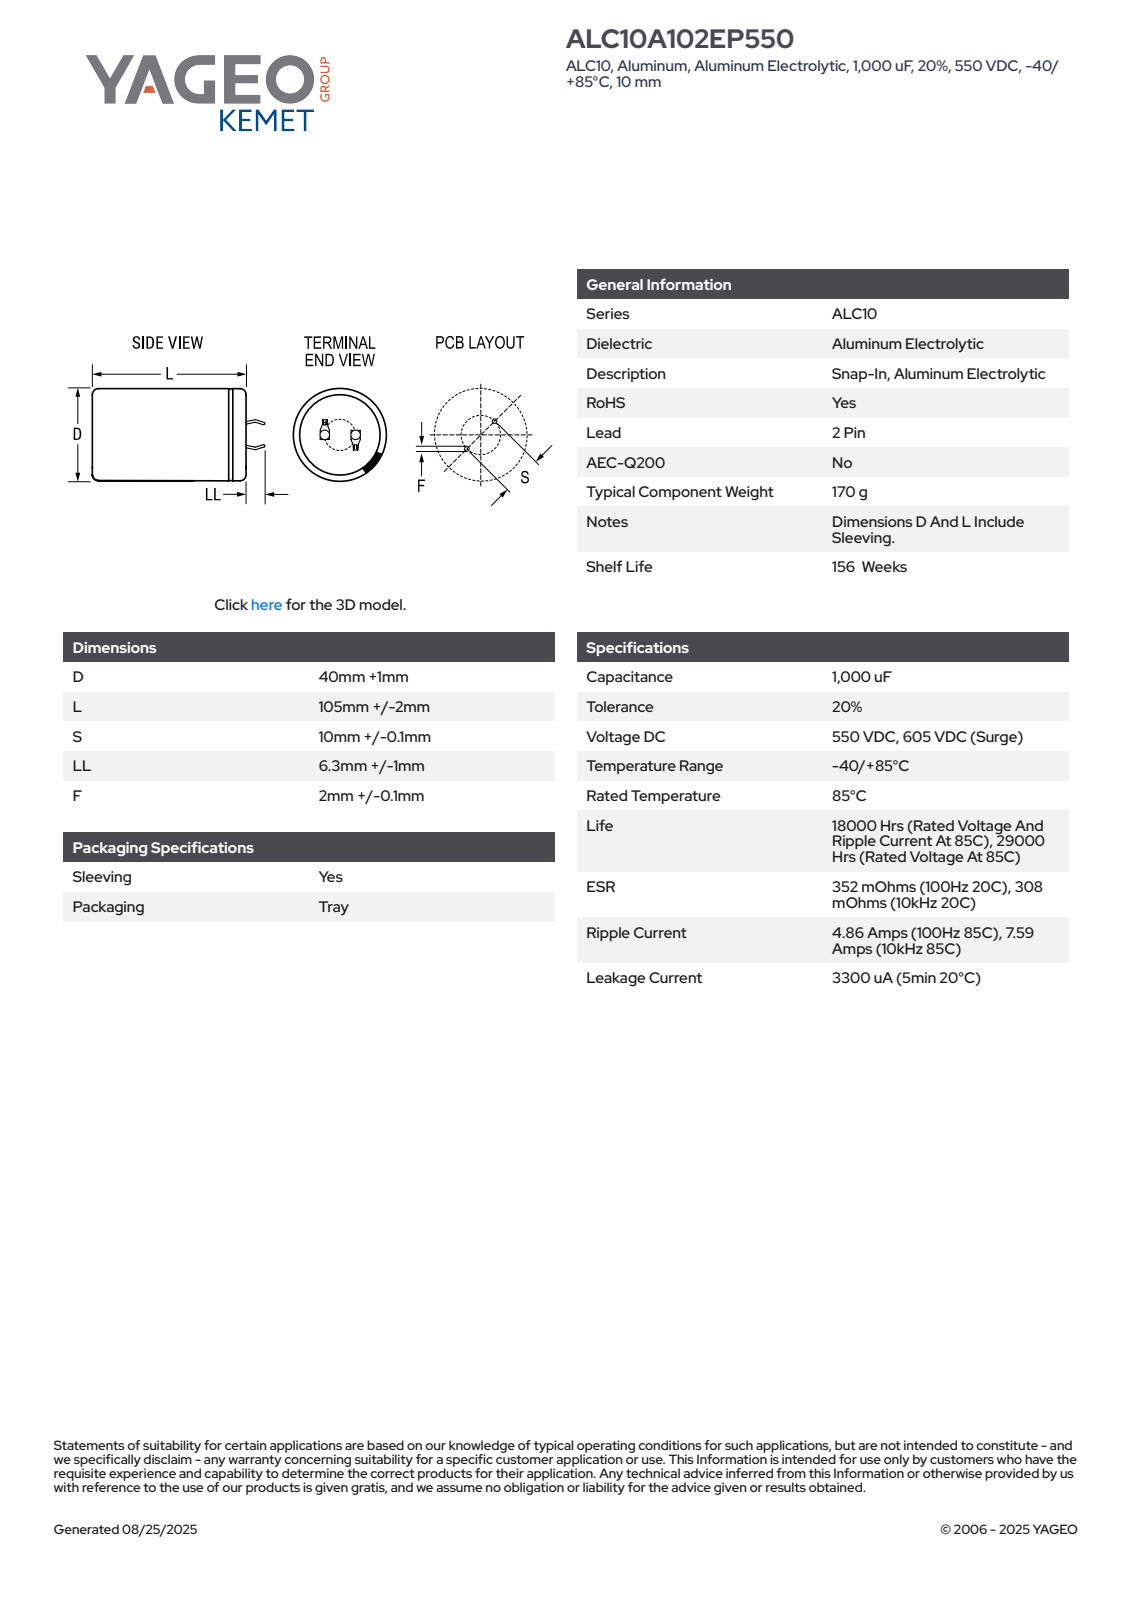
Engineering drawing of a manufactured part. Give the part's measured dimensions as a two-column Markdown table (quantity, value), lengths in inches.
| quantity | value |
| --- | --- |
| part name | CARS_K2P_40X105_D41L107S10LL7.3F2.1 |
| STEP written by | SolidWorks 2014 (AUTOMOTIVE_DESIGN) |
| units | inches |
| bodies | 1 solid, 100 faces (52 planar, 9 cylindrical, 39 other) |
| overall size | 4.5 × 1.614 × 1.614 |
| volume | 8.573 in³ |
| surface area | 25.43 in² |
| round holes (diameter × count) | 1.428 × 1 |
| round bosses / shafts (diameter × count) | 1.614 × 1 |
| partial cylindrical surfaces (radius × count) | 0.807 × 1 |
| main face-to-face distances | 4.212, 0.024, 4.232, 0.02, 0.279, 0.301, 0.03, 0.053, 0.302, 0.255 |
